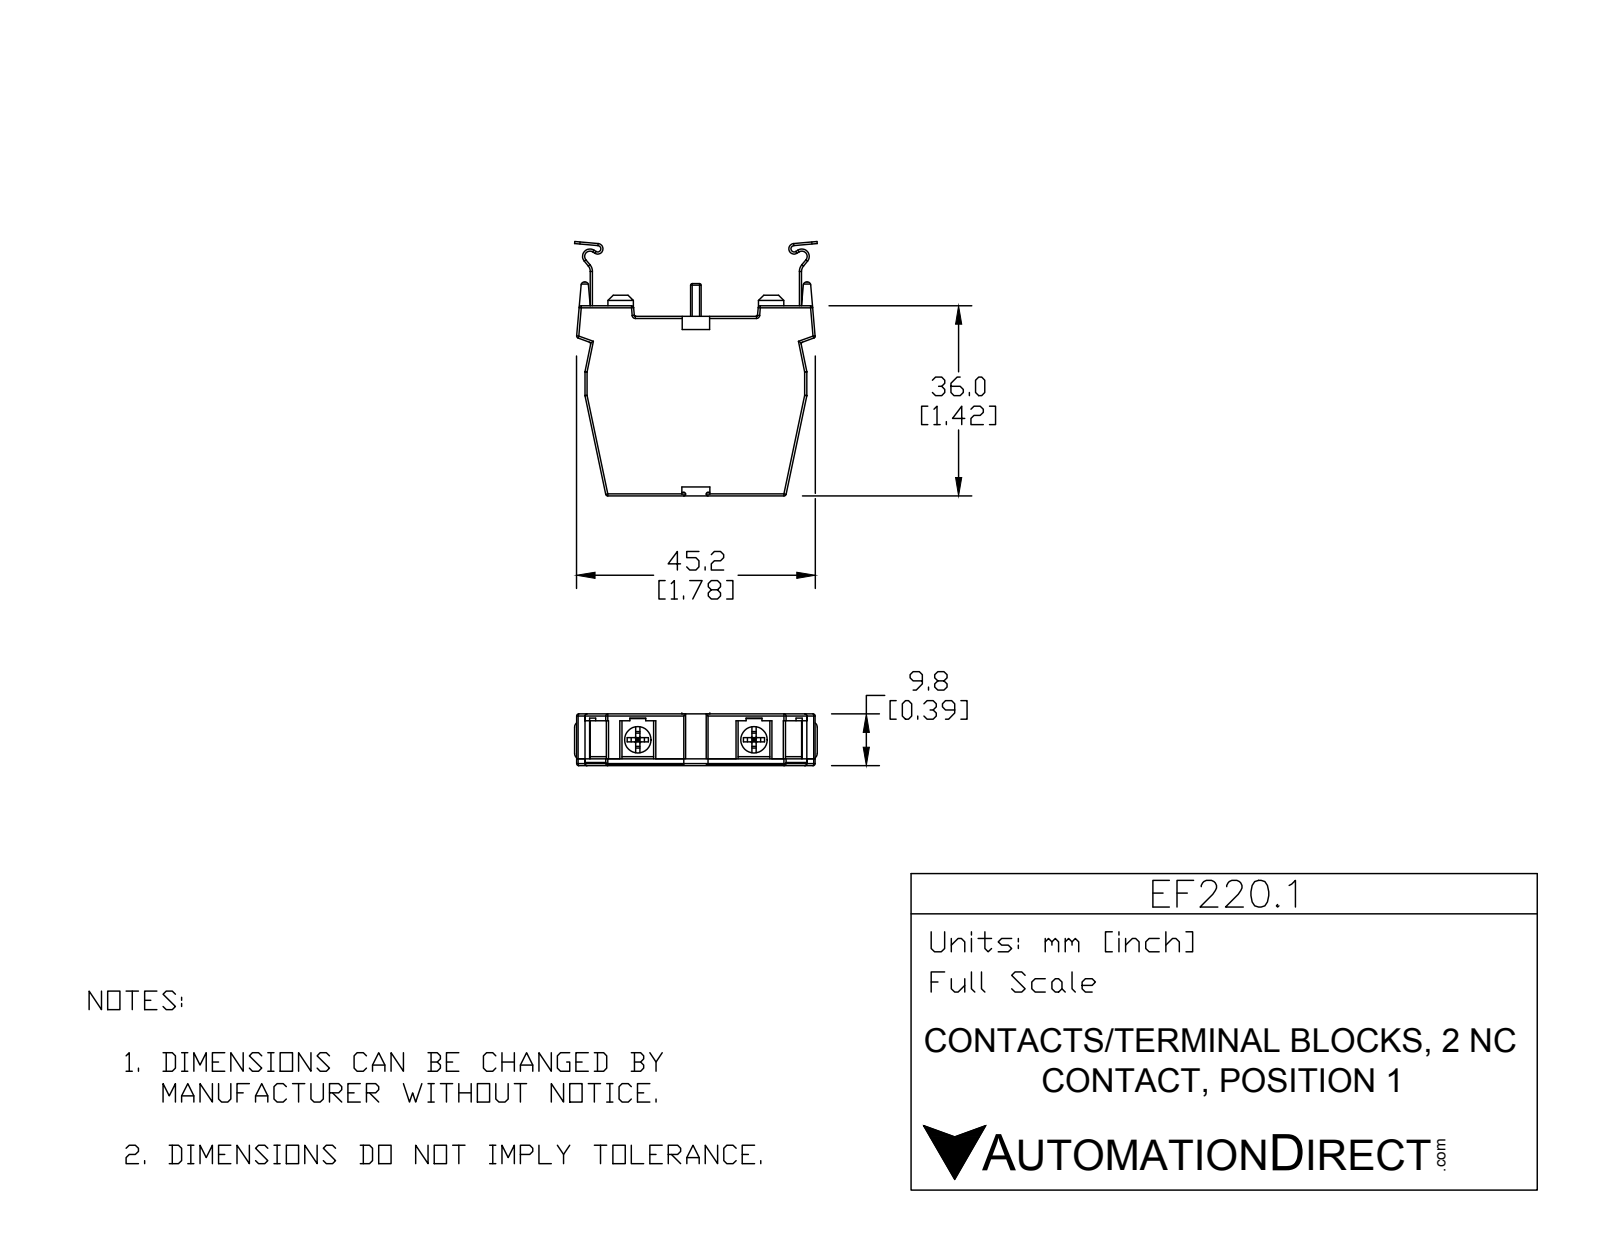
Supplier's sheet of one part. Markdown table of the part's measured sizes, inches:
| quantity | value |
| --- | --- |
| part name | EF220.1 |
| STEP written by | SolidWorks 2015 (AUTOMOTIVE_DESIGN) |
| units | inches |
| bodies | 7 solids, 299 faces (173 planar, 104 cylindrical, 22 other) |
| overall size | 1.896 × 1.822 × 0.386 |
| volume | 0.741 in³ |
| surface area | 10.24 in² |
| round holes (diameter × count) | 0.197 × 4 |
| round bosses / shafts (diameter × count) | 0.157 × 4, 0.187 × 2 |
| partial cylindrical surfaces (radius × count) | 0.01 × 44, 0.02 × 8, 0.039 × 6, 0.024 × 4, 0.024 × 2, 0.039 × 2, 0.055 × 2, 0.063 × 2 |
| main face-to-face distances | 0.386, 0.055, 0.331, 1.339, 0.276, 0.079, 0.016, 0.125, 1.464, 1.417 |
| hole center spacings | 0.859 |
